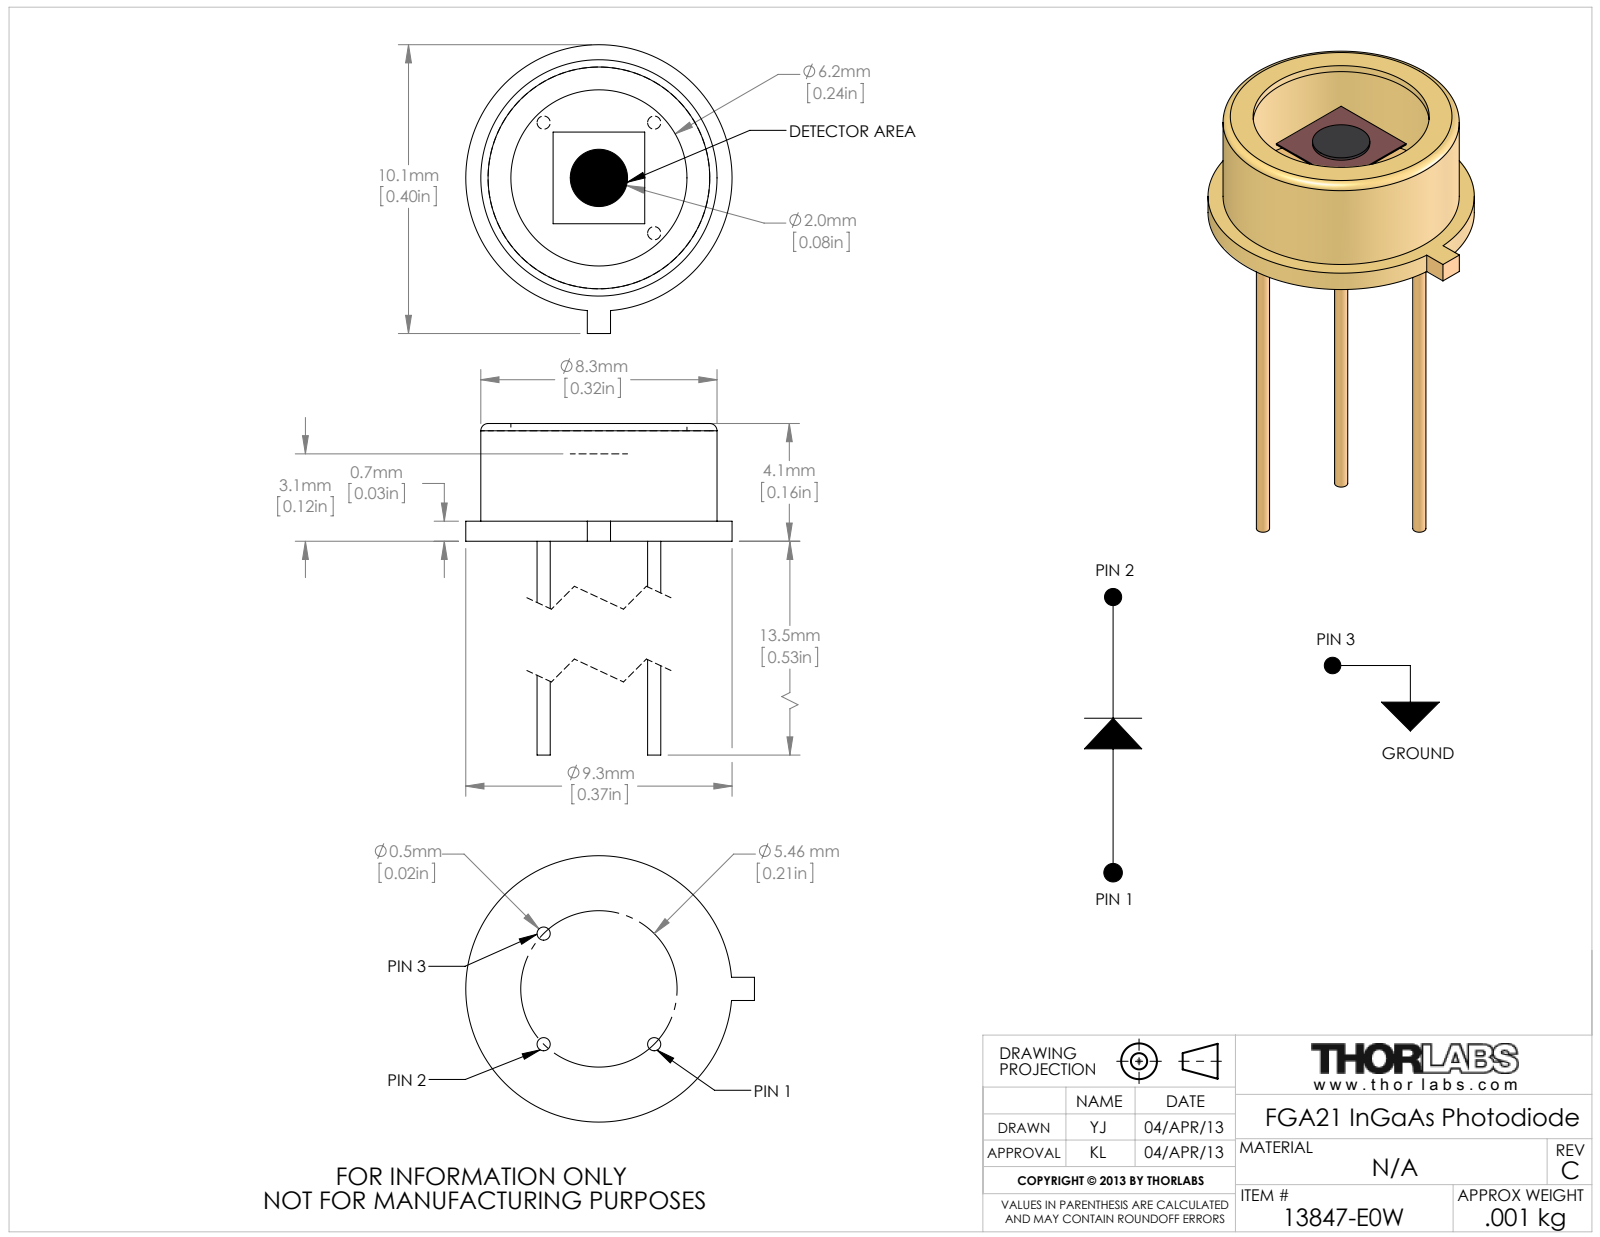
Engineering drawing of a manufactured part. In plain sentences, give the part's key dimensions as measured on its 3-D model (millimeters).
The part is named "13847-E0W". Its 3-D file was written by "SolidWorks 2012 (AUTOMOTIVE_DESIGN)". It is 2 solids with 37 faces: 18 planar, 17 cylindrical and 2 other. Overall it measures 17.61 by 10.08 by 9.3 millimeters. Its volume is 69 cubic millimeters and its surface area 447 square millimeters. Round holes: 1 of diameter 6.15, 1 of diameter 7.74. Round bosses or shafts: 3 of diameter 0.46, 1 of diameter 9.3, 1 of diameter 8.25, 1 of diameter 2. The main face-to-face distances are 0.45, 3.41, 3.86, 4.11, 3.66, 0.7, 3.16, 2.9, 2.45, 2.2.
